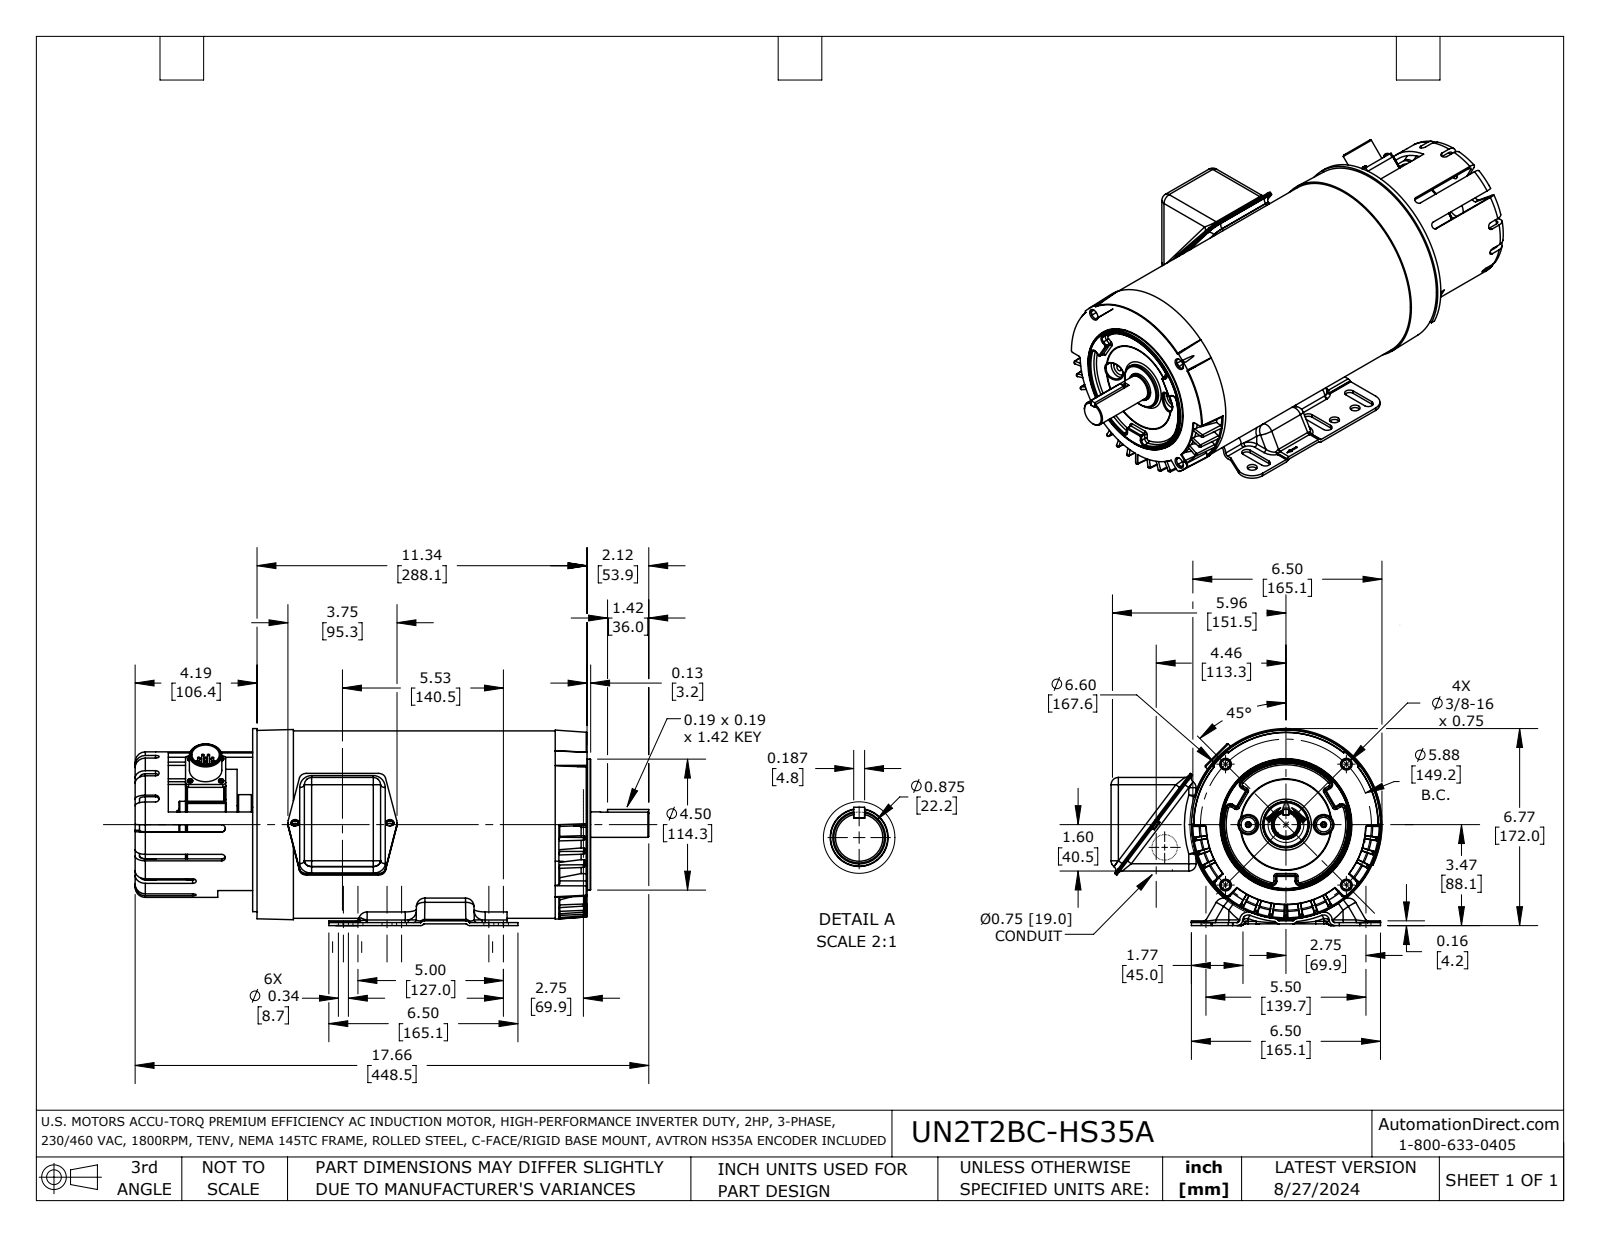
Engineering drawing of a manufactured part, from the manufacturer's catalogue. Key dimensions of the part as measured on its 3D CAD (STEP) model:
Part name (STEP PRODUCT): UN2T2BC-HS35A
STEP written by: SolidWorks 2021 (AUTOMOTIVE_DESIGN)
Units: inches
Bodies: 26 solids, 3050 faces (756 planar, 717 cylindrical, 1577 other)
Overall size (bounding box): 17.656 × 9.311 × 6.77
Volume: 105.4 in³ · Surface area: 1 211 in²
Round holes (diameter × count): ⌀0.25 ×8, ⌀0.344 ×6, ⌀0.4 ×6, ⌀0.12 ×4, ⌀0.2 ×4, ⌀0.302 ×4, ⌀0.421 ×4, ⌀0.55 ×4, ⌀0.136 ×3, ⌀0.098 ×2, ⌀0.173 ×2, ⌀0.229 ×2
Round bosses / shafts (diameter × count): ⌀0.072 ×8, ⌀0.175 ×4, ⌀0.12 ×4, ⌀0.15 ×3, ⌀0.325 ×2, ⌀0.072 ×2, ⌀6.44 ×1, ⌀6.315 ×1
Partial cylindrical surfaces — rounded edges, fillets, slot ends (radius × count): R0.062 ×91, R0.031 ×71, R0.125 ×42, R0.25 ×26, R0.202 ×18, R0.094 ×13, R0.048 ×12, R0.172 ×12
Main face-to-face distances: 0.048, 1.08, 1.375, 2.455, 0.15, 4.04, 0.104, 0.12, 0.53, 0.06
Hole centre spacings: 2.098, 2.246, 3.419, 4.349, 5.422, 2.073, 2.232, 2.234
